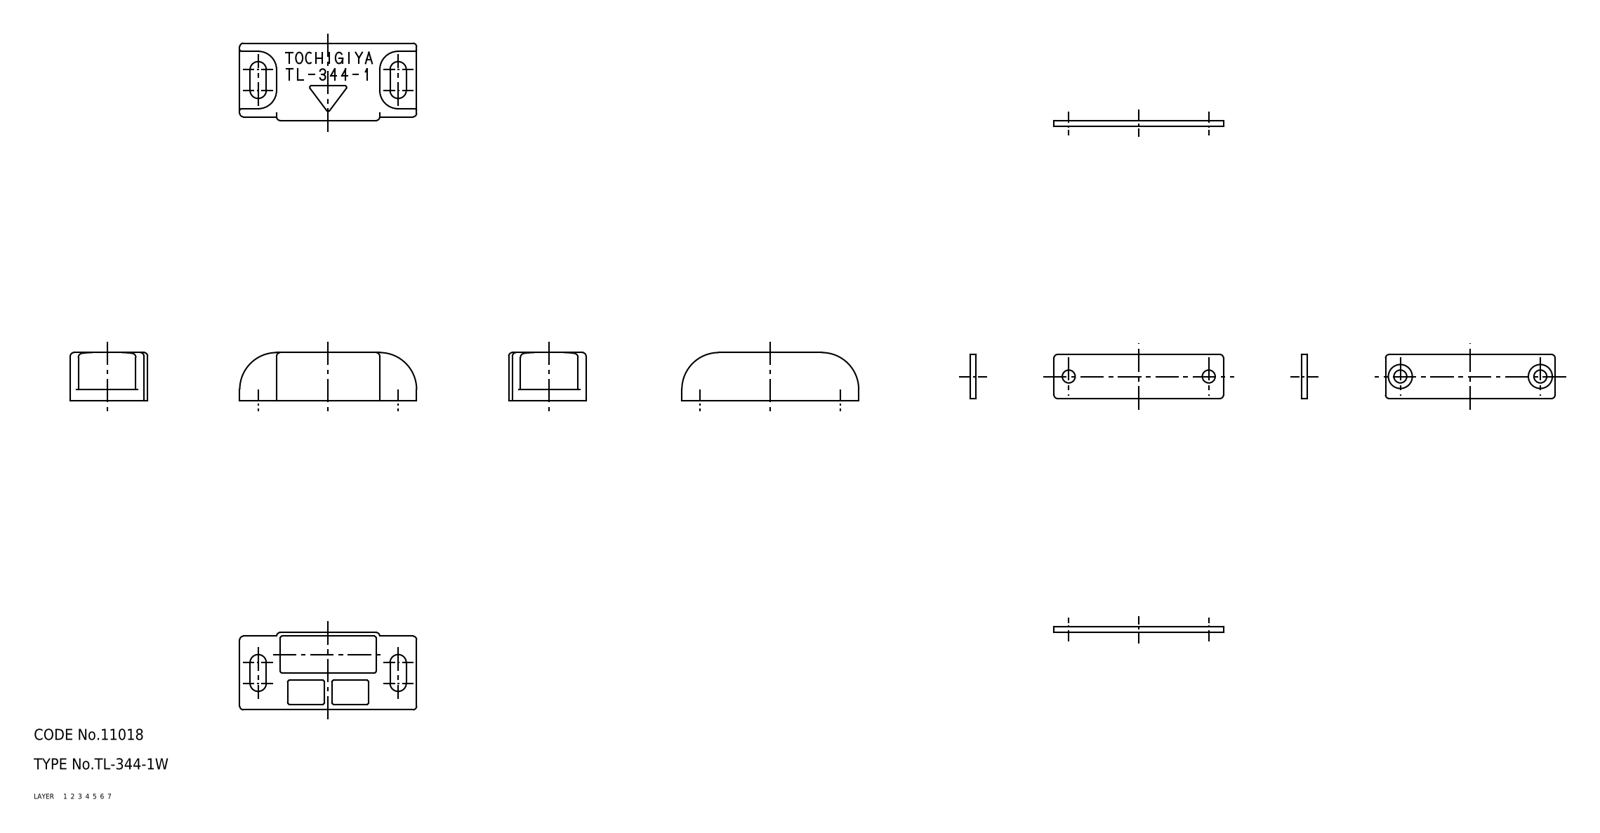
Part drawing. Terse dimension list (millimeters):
name: 67114864; 67114877; 67114890
written by: CADfix (AUTOMOTIVE_DESIGN)
unit: mm
bodies: 3 solids, 122 faces (0 planar, 0 cylindrical, 122 other)
size: 48 × 35.5 × 13
volume: 8 929 mm³; area: 6 545 mm²
